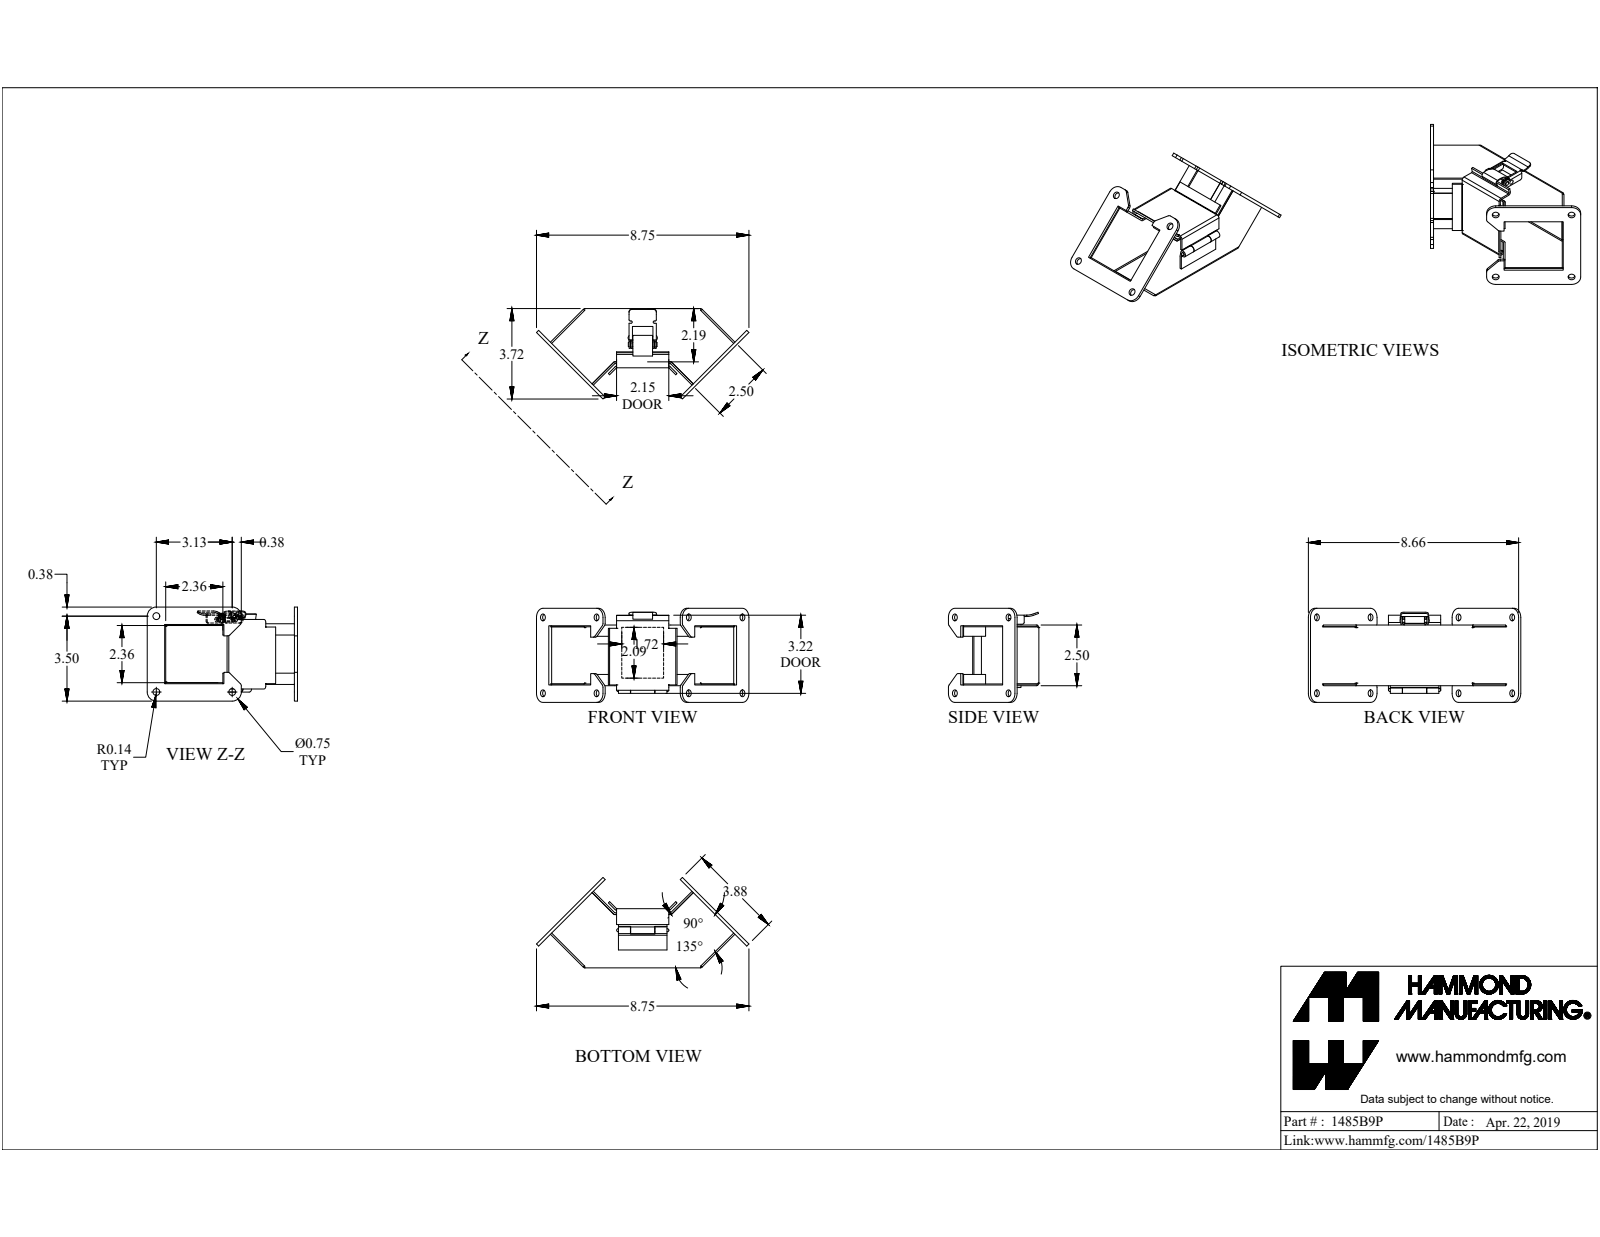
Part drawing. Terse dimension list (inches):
name: 1485B9P
written by: SolidWorks 2019 (CONFIG_CONTROL_DESIGN)
unit: in
bodies: 12 solids, 318 faces (212 planar, 100 cylindrical, 6 other)
size: 8.751 × 3.875 × 3.725
volume: 7.165 in³; area: 193.5 in²
holes: 8× ⌀0.281, 1× ⌀0.125, 1× ⌀0.164
bosses: 1× ⌀0.275, 1× ⌀0.162, 1× ⌀0.158, 1× ⌀0.125, 1× ⌀0.125
rounds: 11× R0.036, 11× R0.108, 11× R0.125, 8× R0.375, 4× R0.029, 4× R0.086, 2× R0.015, 2× R0.047
face distances: 0.072, 2.428, 2.356, 2.5, 0.125, 2.366, 5.427, 5.302, 5.499, 5.374
hole spacings: 3.125, 3.125, 4.419, 2.928
